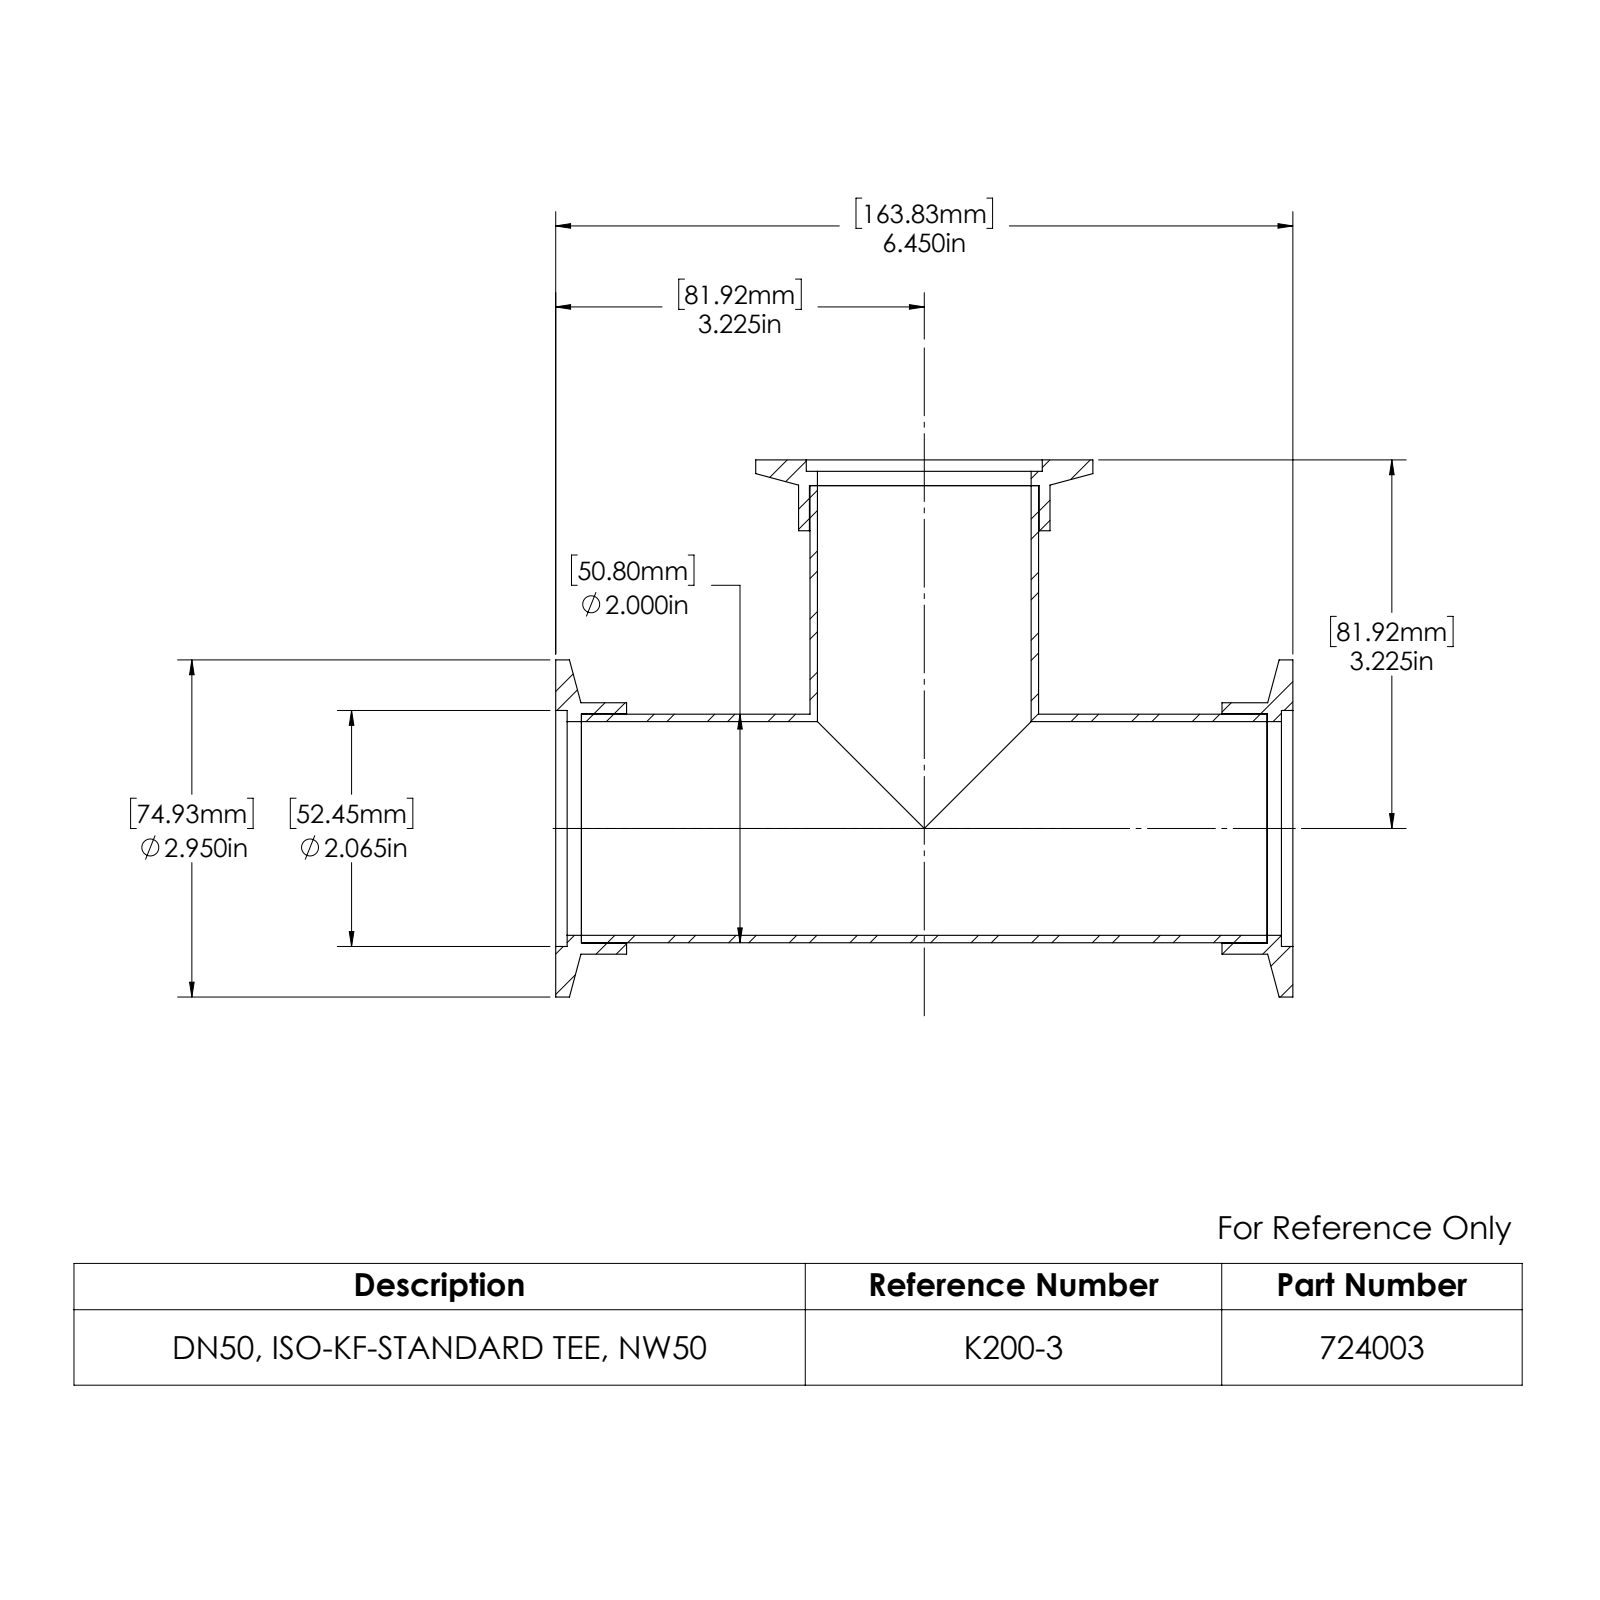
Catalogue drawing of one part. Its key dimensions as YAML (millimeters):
part_name: "404503; 713004; 724003"
step_written_by: "SolidWorks 2022 (AUTOMOTIVE_DESIGN)"
units: millimeters
bodies: {solids: 4, faces: 59, planar: 15, cylindrical: 38, other: 6}
overall_size: [163.8, 119.4, 74.9]
volume: 96220
surface_area: 92710
round_holes:
  - {diameter: 47.5, count: 2}
  - {diameter: 51.1, count: 2}
  - {diameter: 52.5, count: 2}
round_bosses_or_shafts:
  - {diameter: 74.9, count: 2}
  - {diameter: 55.9, count: 2}
  - {diameter: 50.8, count: 2}
face_to_face_distances: [163.8, 15.7, 2.5, 13.2, 5.7, 148.1, 10, 161.3, 3.2, 145.5]
